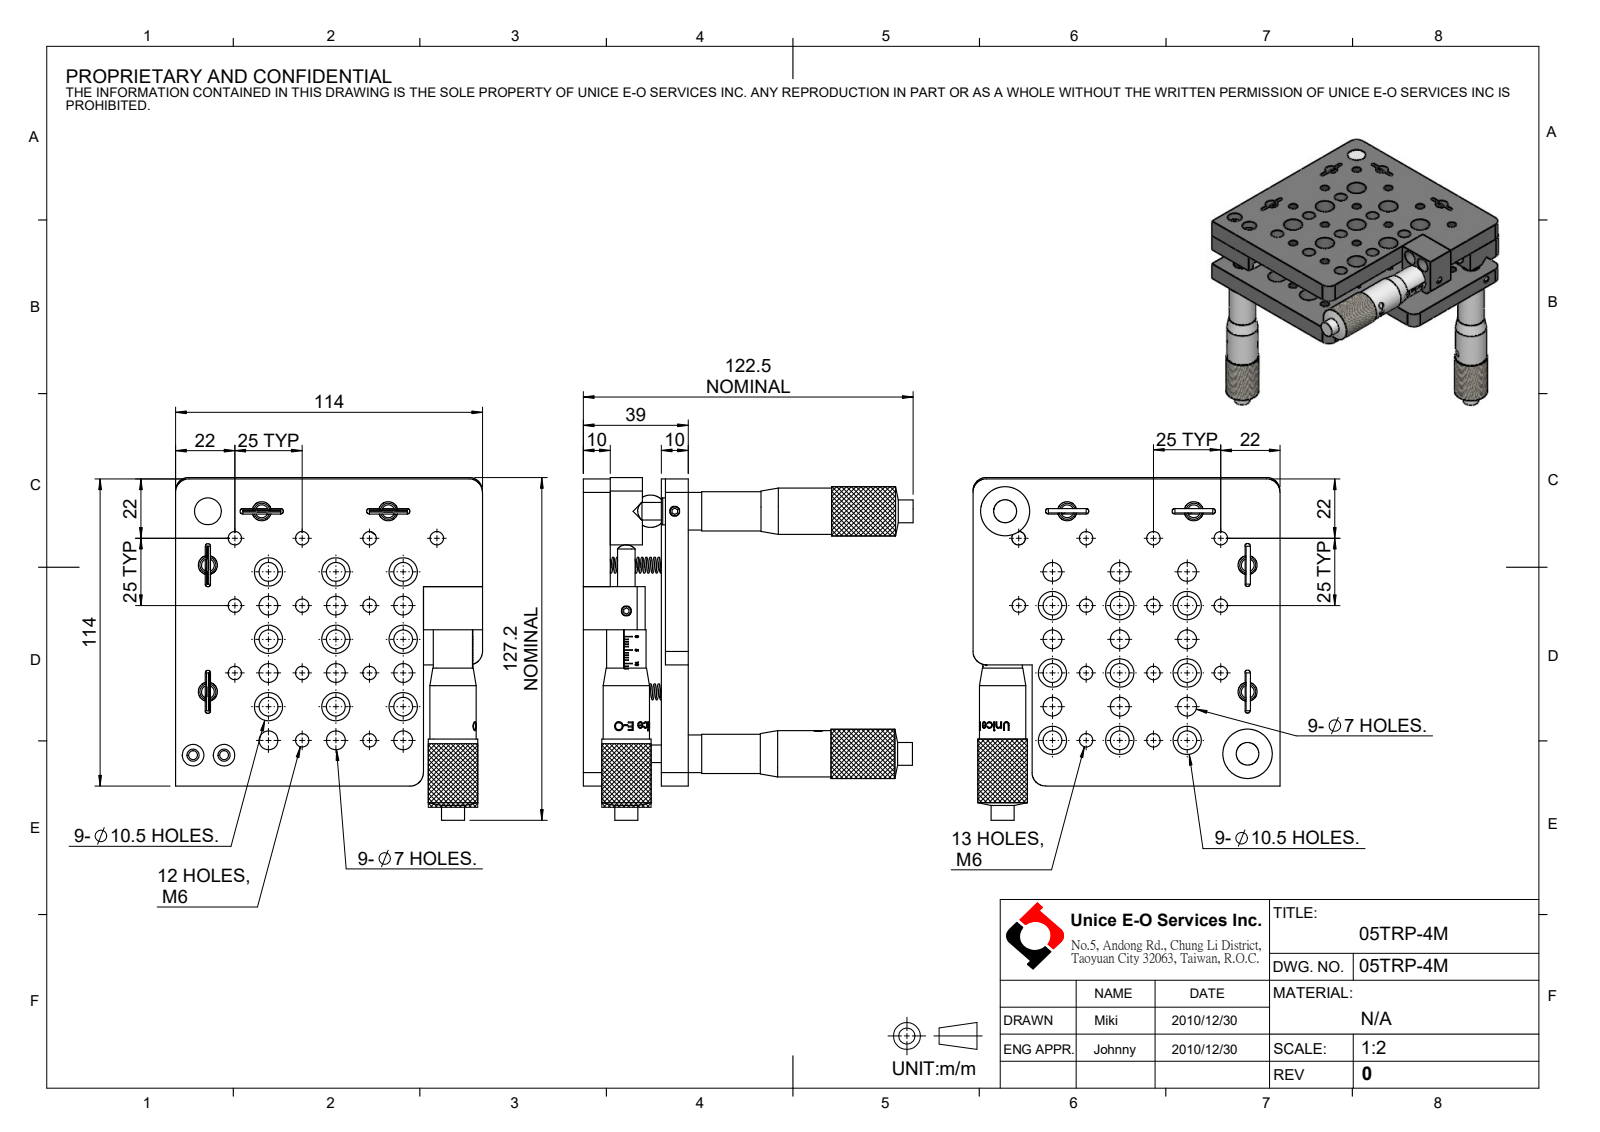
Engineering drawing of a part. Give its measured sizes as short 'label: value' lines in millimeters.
name: 05TRP-4M
written by: SolidWorks 2016 (CONFIG_CONTROL_DESIGN)
unit: mm
bodies: 32 solids, 1778 faces (995 planar, 358 cylindrical, 425 other)
size: 127.2 × 122.46 × 114
volume: 285 993 mm³; area: 118 040 mm²
holes: 23× ⌀7, 18× ⌀10.5, 13× ⌀5, 7× ⌀3.3, 5× ⌀10, 4× ⌀1.2, 4× ⌀4.5, 4× ⌀8, 3× ⌀6.3, 3× ⌀14.65, 1× ⌀1.7, 1× ⌀2.5
bosses: 4× ⌀1.6, 4× ⌀0.6, 3× ⌀18.3, 3× ⌀17.2, 3× ⌀14.6, 3× ⌀9.75, 3× ⌀8.5, 3× ⌀6.5
rounds: 8× R1, 6× R5, 3× R8.55
face distances: 29, 10, 39, 19, 22, 114, 8.5, 7, 17, 12
hole spacings: 27.95, 25, 39.53, 55.9, 17.68, 12.5, 35.36, 45.07
